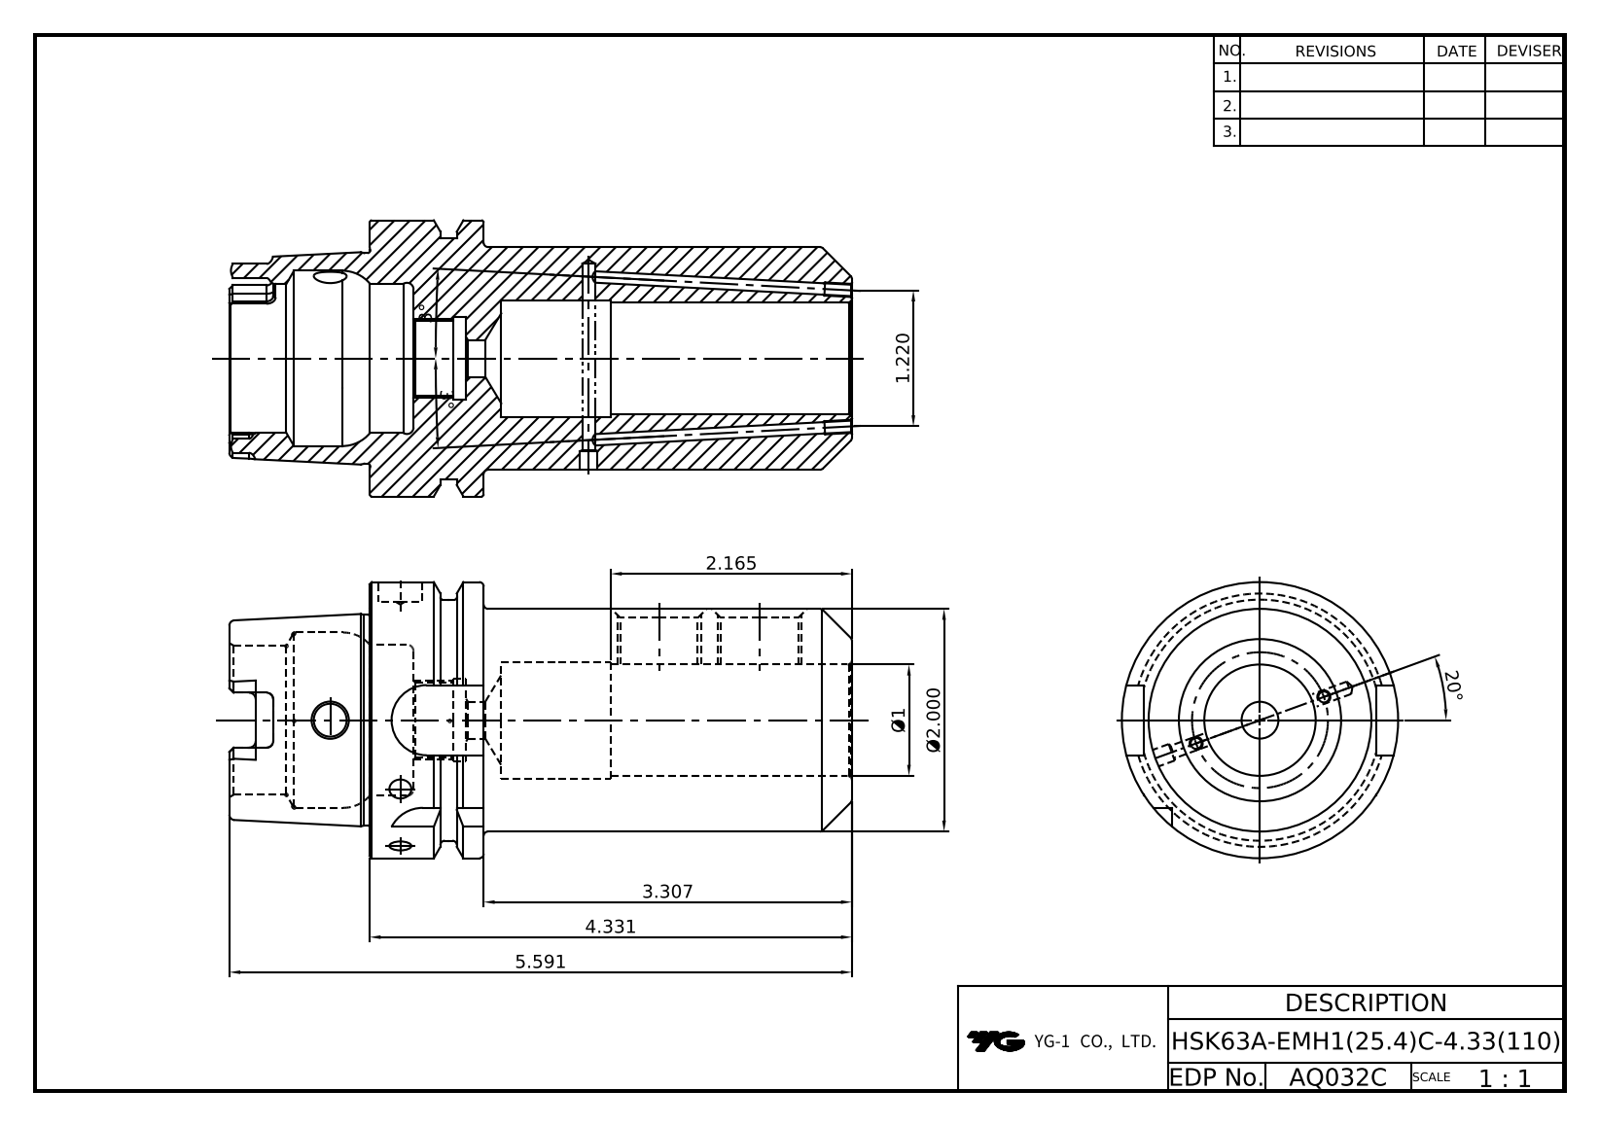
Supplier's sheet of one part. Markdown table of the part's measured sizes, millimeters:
| quantity | value |
| --- | --- |
| part name | LO-HSK63A-EMH 25.4C-4.33 |
| STEP written by | Autodesk Inventor 2024 (AUTOMOTIVE_DESIGN) |
| units | millimeters |
| bodies | 1 solid, 121 faces (42 planar, 37 cylindrical, 42 other) |
| overall size | 142 × 63 × 63 |
| volume | 199 490 mm³ |
| surface area | 42 998 mm² |
| round holes (diameter × count) | 2.46 × 2, 17.32 × 2, 7.5 × 1, 8 × 1, 10 × 1, 16.92 × 1, 19 × 1, 25.4 × 1, 26.6 × 1, 34 × 1, 40 × 1 |
| round bosses / shafts (diameter × count) | 63 × 1, 55 × 1, 50.8 × 1, 48.04 × 1 |
| partial cylindrical surfaces (radius × count) | 1.5 × 6, 2.88 × 4, 8 × 4 |
| main face-to-face distances | 26, 4, 10, 16, 110, 100, 84, 30, 20, 80 |
| hole center spacings | 22.9, 59, 81.9 |
